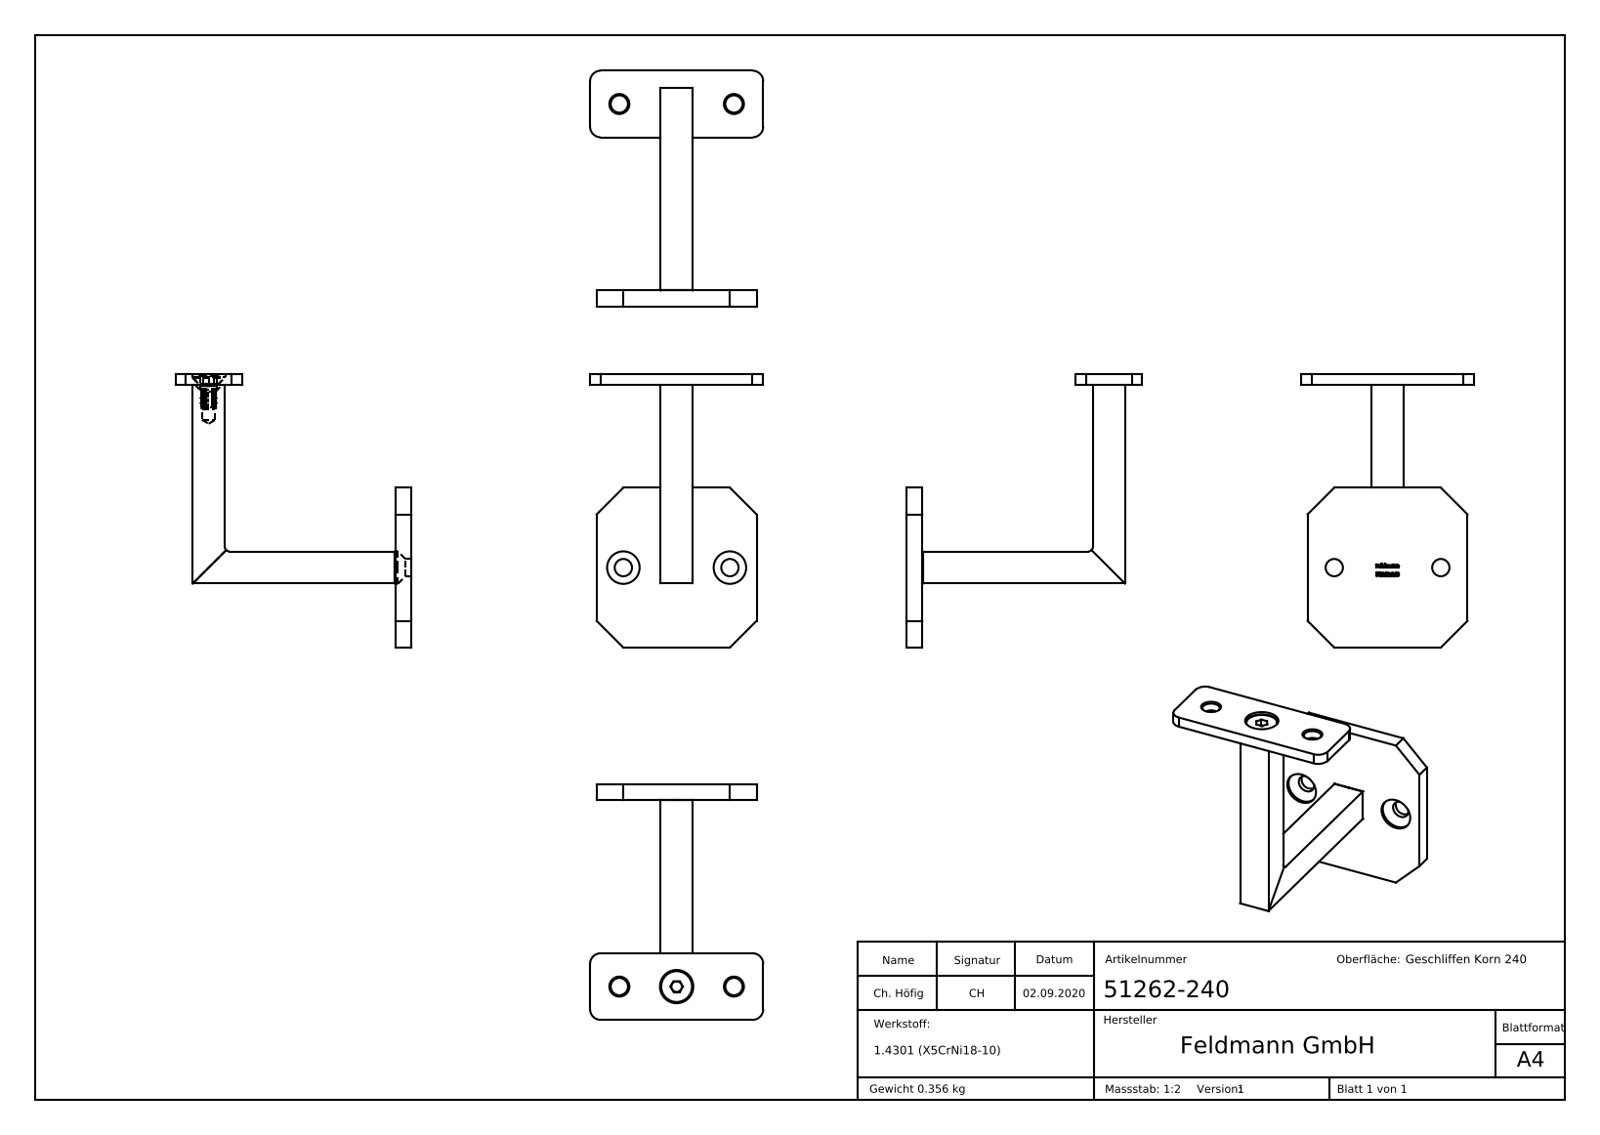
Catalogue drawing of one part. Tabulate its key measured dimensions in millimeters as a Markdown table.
| quantity | value |
| --- | --- |
| part name | 5126X-XXX Teil3; DIN 7380 M5x8_M5x8; 5126X-XXX Teil1; 51262-240 (+7 more) |
| STEP written by | SolidWorks 2018 (CONFIG_CONTROL_DESIGN) |
| units | millimeters |
| bodies | 5 solids, 435 faces (189 planar, 74 cylindrical, 172 other) |
| overall size | 102.5 × 88.5 × 65 |
| volume | 47 875 mm³ |
| surface area | 21 456 mm² |
| round holes (diameter × count) | 6.5 × 4, 12.2 × 2, 5 × 1, 5.5 × 1, 7 × 1, 10 × 1, 12.5 × 1 |
| round bosses / shafts (diameter × count) | 11.57 × 1, 6 × 1, 4.02 × 1 |
| partial cylindrical surfaces (radius × count) | 4 × 4, 2 × 1, 6 × 1 |
| main face-to-face distances | 12, 6, 4, 76, 82, 78.5, 70, 24, 36, 74.5 |
| hole center spacings | 21.5, 52, 40, 43 |
